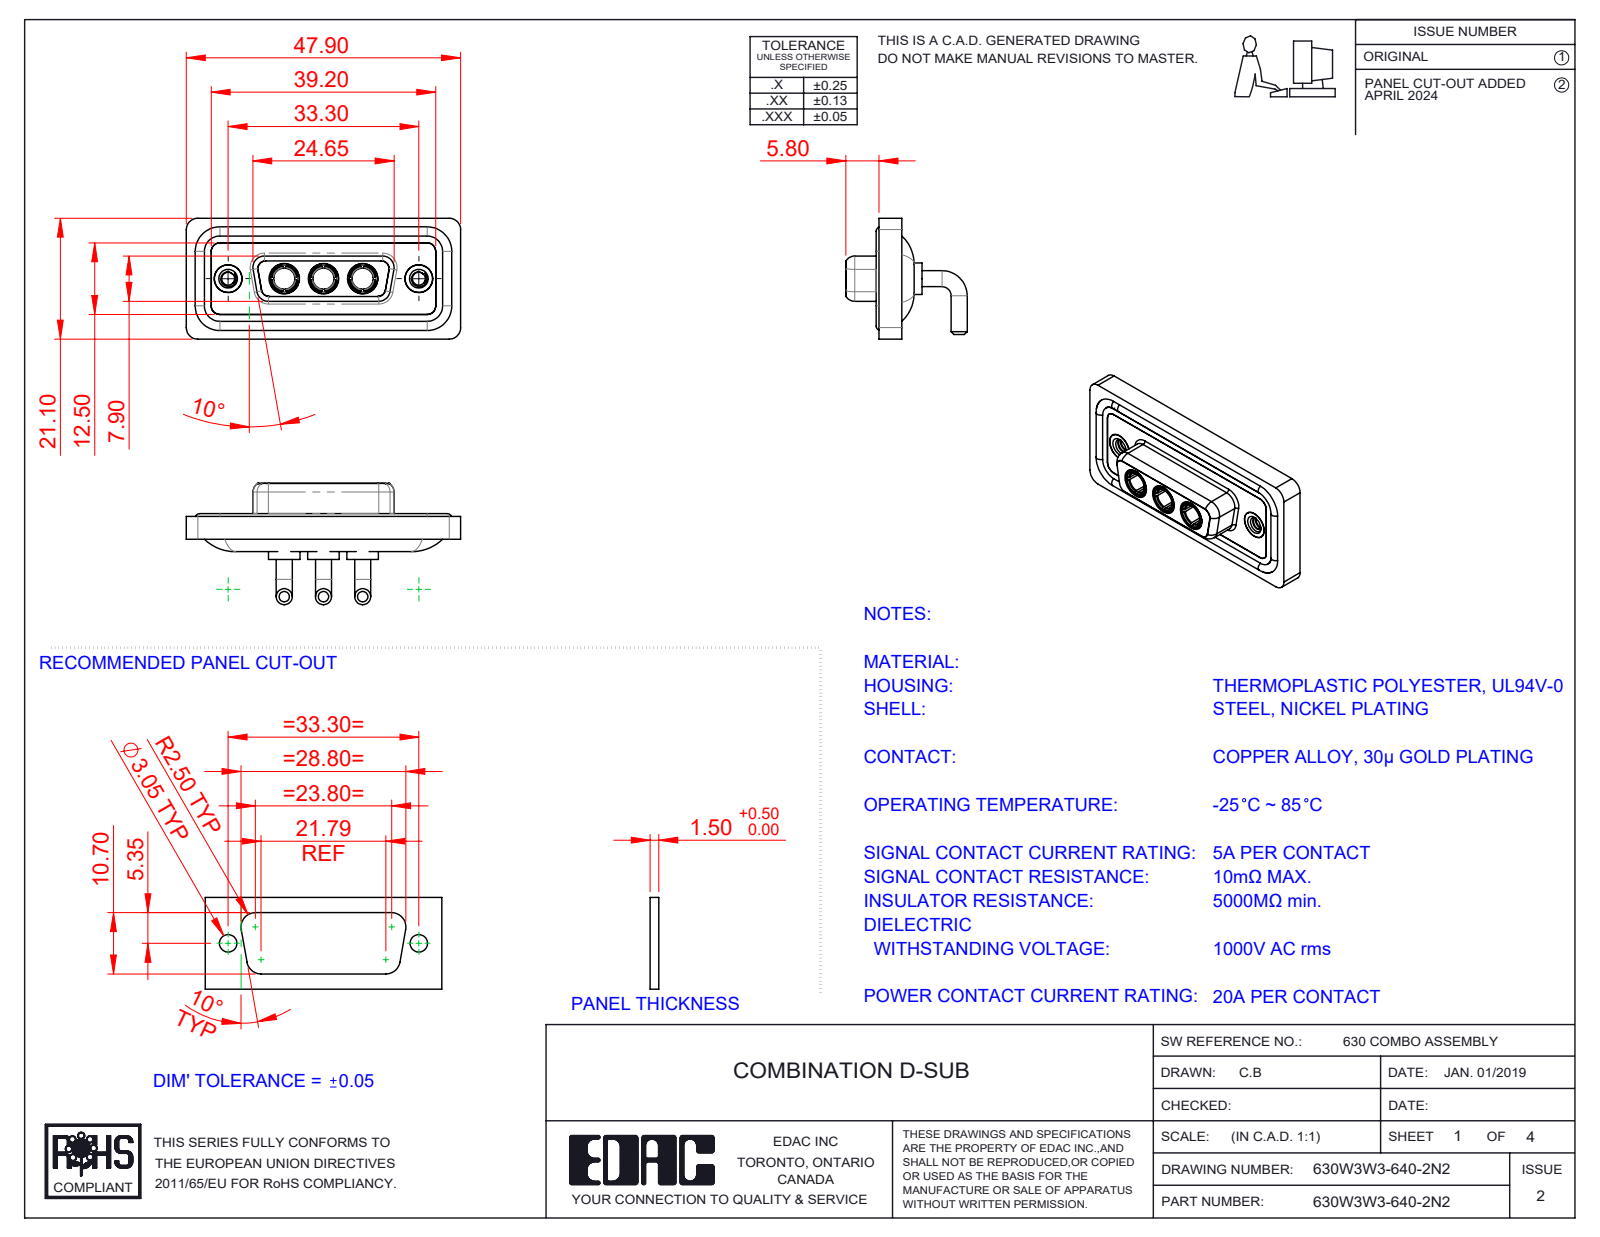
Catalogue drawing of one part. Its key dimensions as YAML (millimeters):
part_name: "630W3W3-640-2N2; Power Socket_20A RA; 630Combo Shell Front_15 Contacts; 630Combo Housing_3W3 (+3 more)"
step_written_by: "SolidWorks 2023 (CONFIG_CONTROL_DESIGN)"
units: millimeters
bodies: {solids: 13, faces: 620, planar: 192, cylindrical: 263, other: 165}
overall_size: [47.9, 21.2, 21.1]
volume: 6180
surface_area: 9971
round_holes:
  - {diameter: 4.85, count: 5}
  - {diameter: 3.7, count: 3}
  - {diameter: 5.3, count: 3}
  - {diameter: 2.26, count: 2}
  - {diameter: 4, count: 2}
  - {diameter: 4.05, count: 2}
  - {diameter: 5, count: 2}
round_bosses_or_shafts:
  - {diameter: 2.8, count: 6}
  - {diameter: 1.6, count: 4}
  - {diameter: 5.5, count: 3}
  - {diameter: 5.2, count: 3}
  - {diameter: 4.96, count: 3}
  - {diameter: 4.75, count: 3}
  - {diameter: 3.75, count: 3}
  - {diameter: 4.95, count: 2}
partial_cylinders:
  - {radius: 2, count: 20}
  - {radius: 1.5, count: 18}
  - {radius: 1.35, count: 12}
  - {radius: 1.6, count: 8}
  - {radius: 0.25, count: 4}
  - {radius: 0.5, count: 4}
  - {radius: 0.6, count: 4}
  - {radius: 0.65, count: 4}
face_to_face_distances: [0.4, 1.8, 1.1, 1.6, 2.9, 2.5, 3.1, 3.7, 4.1, 1.5]
hole_center_spacings: [6.85, 9.8, 16.65, 23.5, 13.7, 33.3]
